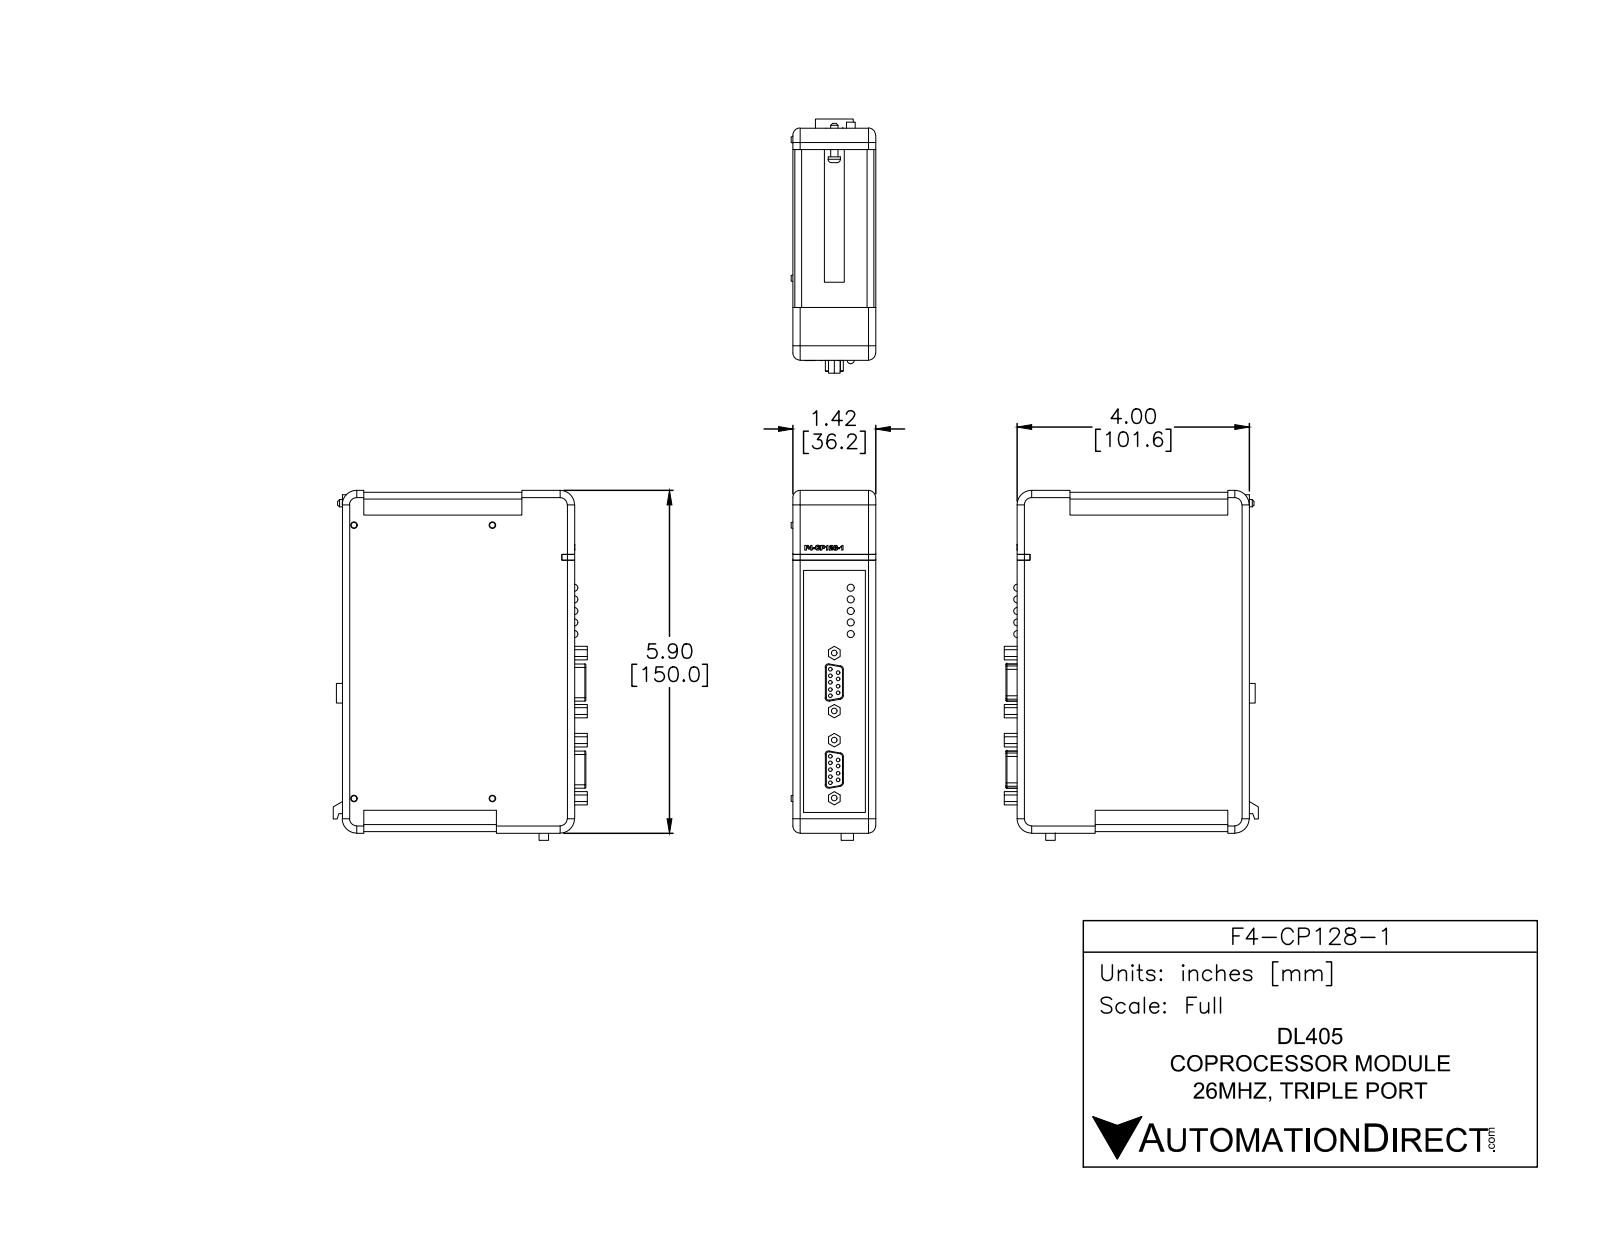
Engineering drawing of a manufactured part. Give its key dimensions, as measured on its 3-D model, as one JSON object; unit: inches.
{"part_name": "F4-CP128-1", "step_written_by": "SolidWorks 2014 (AUTOMOTIVE_DESIGN)", "units": "inches", "bodies": {"solids": 2, "faces": 406, "planar": 221, "cylindrical": 104, "other": 81}, "overall_size": [5.905, 4.375, 1.455], "volume_in3": 32.49, "surface_area_in2": 81.89, "round_holes": [[0.065, 10], [0.065, 8], [0.1, 4]], "round_bosses_or_shafts": [[0.125, 5], [0.212, 1], [0.123, 1]], "partial_cylinders_radius": [[0.06, 8], [0.125, 8], [0.015, 6], [0.12, 4], [0.25, 4], [0.145, 1], [0.171, 1]], "face_to_face_distances": [1.425, 0.03, 3.97, 1.395, 5.875, 5.845, 4, 0.2, 3.77, 3.8], "hole_center_spacings": [1.5, 0.113, 0.125, 0.144, 0.146, 0.32, 0.322, 0.103]}
